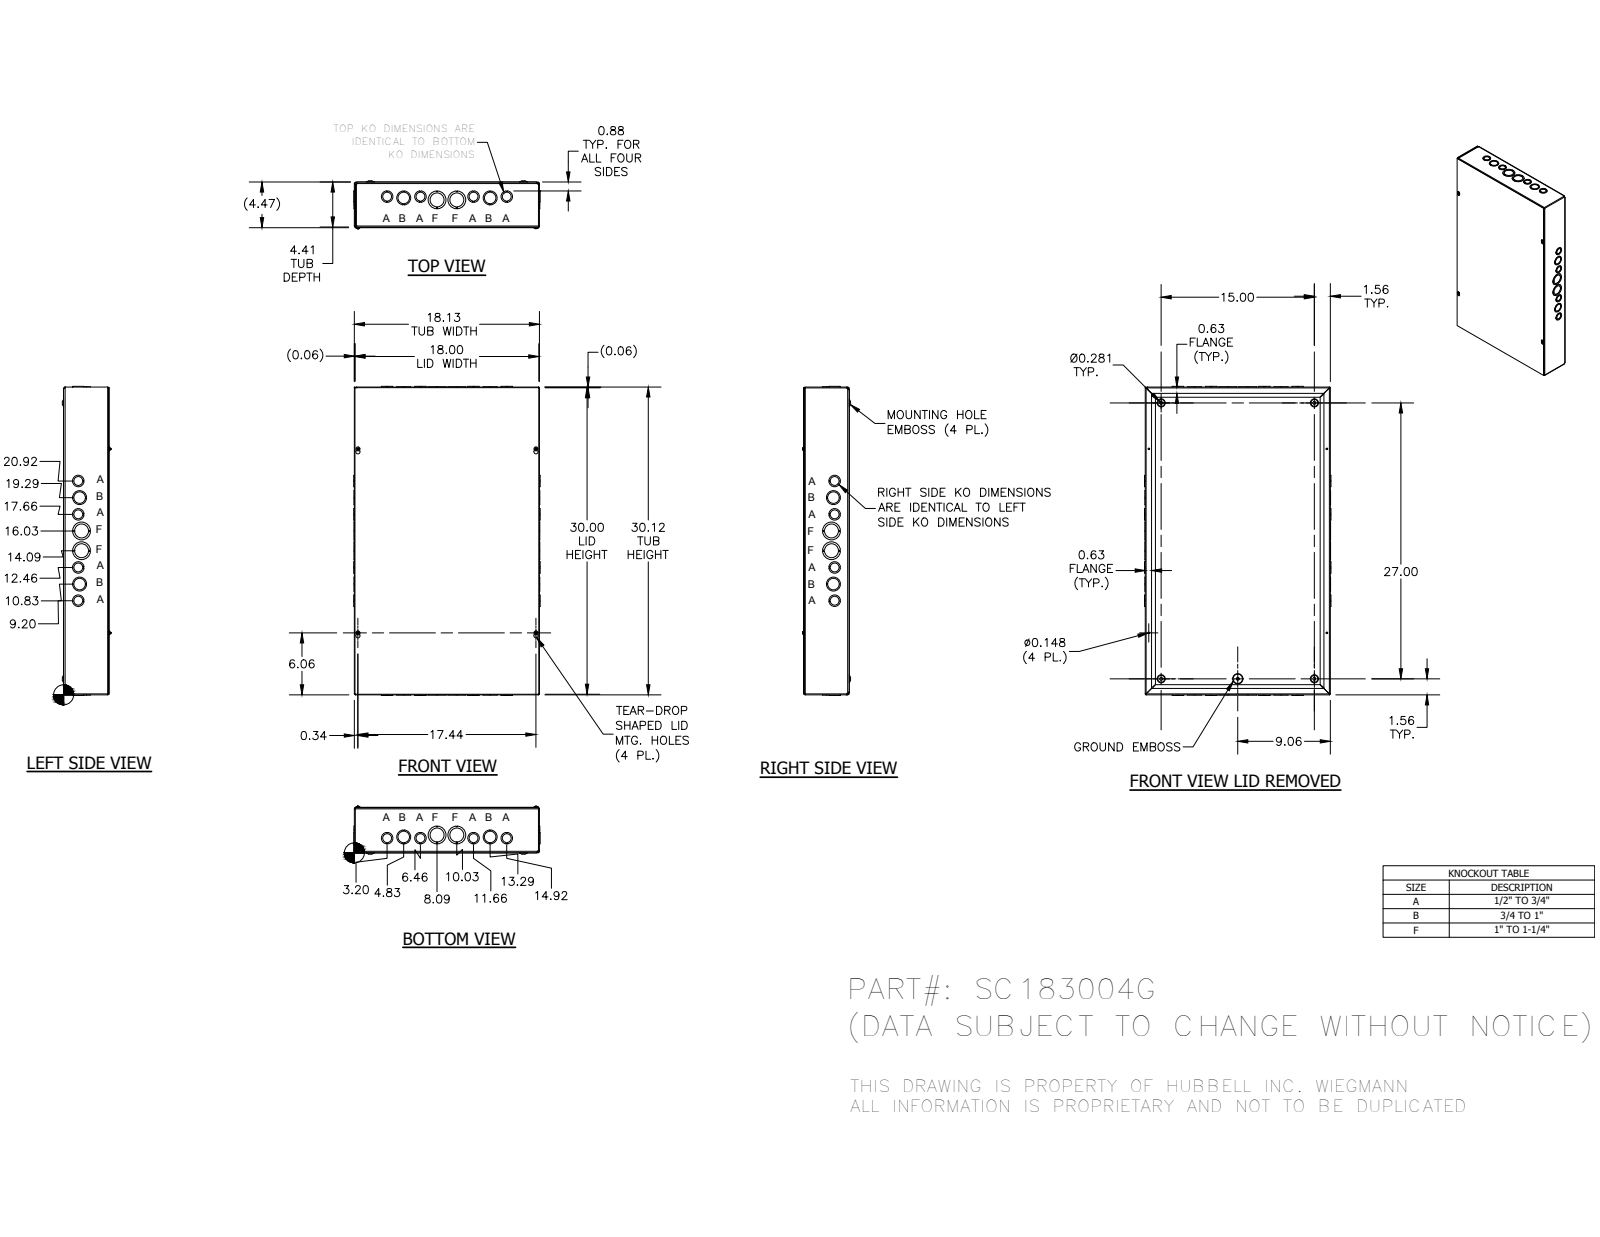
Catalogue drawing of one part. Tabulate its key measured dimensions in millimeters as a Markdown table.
| quantity | value |
| --- | --- |
| part name | SC1830GBKP; SC183004GWRA; SC1830GLID; 34056 (+1 more) |
| STEP written by | Autodesk Inventor 2014 (AUTOMOTIVE_DESIGN) |
| units | millimeters |
| bodies | 38 solids, 1254 faces (838 planar, 265 cylindrical, 151 other) |
| overall size | 768.33 × 463.52 × 119.2 |
| round holes (diameter × count) | 28.57 × 12, 22.22 × 8, 34.92 × 8, 3.76 × 4, 7.62 × 4, 44.45 × 4, 4.19 × 1 |
| round bosses / shafts (diameter × count) | 9.75 × 4, 4.17 × 4, 5.8 × 1 |
| partial cylindrical surfaces (radius × count) | 0.79 × 8, 2.37 × 8, 1.4 × 4, 1.57 × 4, 2.38 × 4, 2.79 × 4, 2.97 × 4, 3.15 × 4 |
| main face-to-face distances | 1.57, 110.32, 111.89, 1.59, 111.91, 113.48, 1.58, 763.6, 460.38, 458.8 |
| hole center spacings | 41.52, 42.15, 82.94, 91.03, 118.42, 132.17, 173.51, 214.88 |
